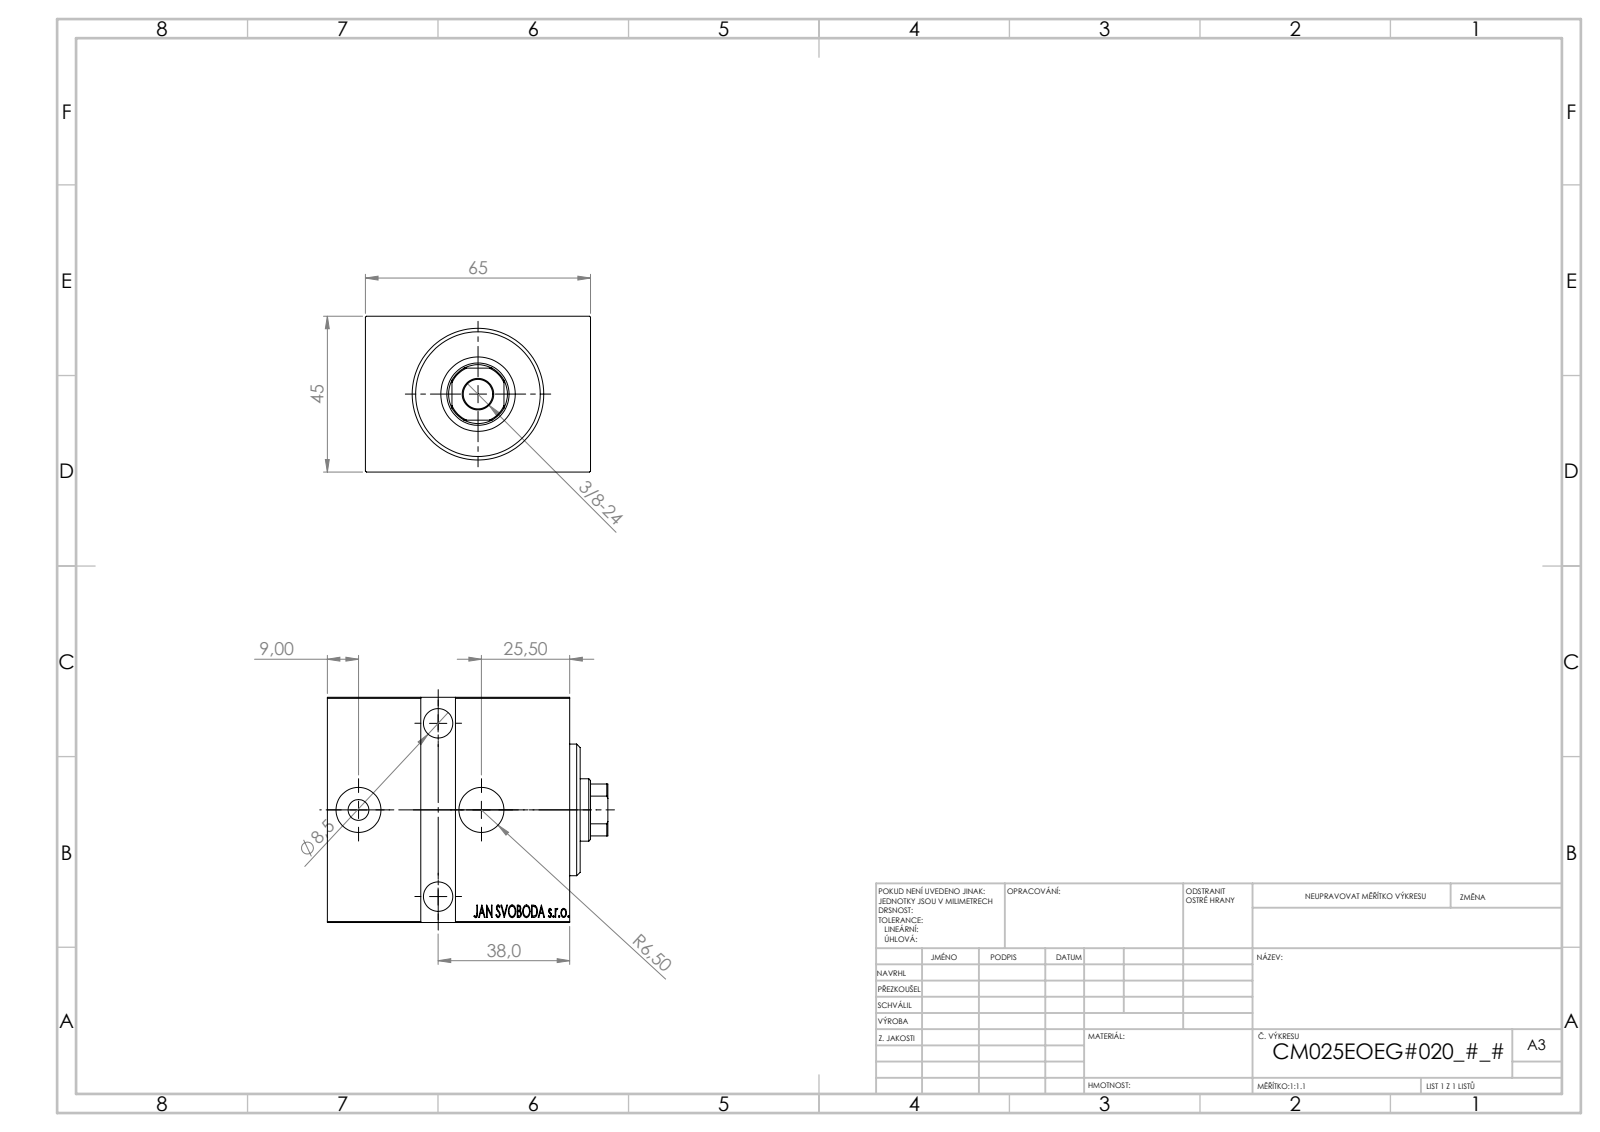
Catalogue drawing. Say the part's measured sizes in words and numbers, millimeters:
The part is named "V450CM_E_VCP; V450CM_E_Body; V450CM_VC_B". Its 3-D file was written by "SolidWorks 2019 (CONFIG_CONTROL_DESIGN)". It is 3 solids with 839 faces: 407 planar, 38 cylindrical and 394 other. Overall it measures 81 by 65 by 45 millimeters. Its volume is 195 046 cubic millimeters and its surface area 39 035 square millimeters. Round holes: 3 of diameter 8.5, 2 of diameter 13, 2 of diameter 13.5, 1 of diameter 18, 1 of diameter 21.5, 1 of diameter 25, 1 of diameter 35. Round bosses or shafts: 1 of diameter 38, 1 of diameter 27, 1 of diameter 6. Partial cylindrical surfaces (rounded edges, fillets, slot ends): 1 of radius 8.5. The main face-to-face distances are 65, 45, 70, 8, 3, 6, 64, 5, 59, 43. The hole center spacings are 27.95, 33.97, 35.5, 50.
